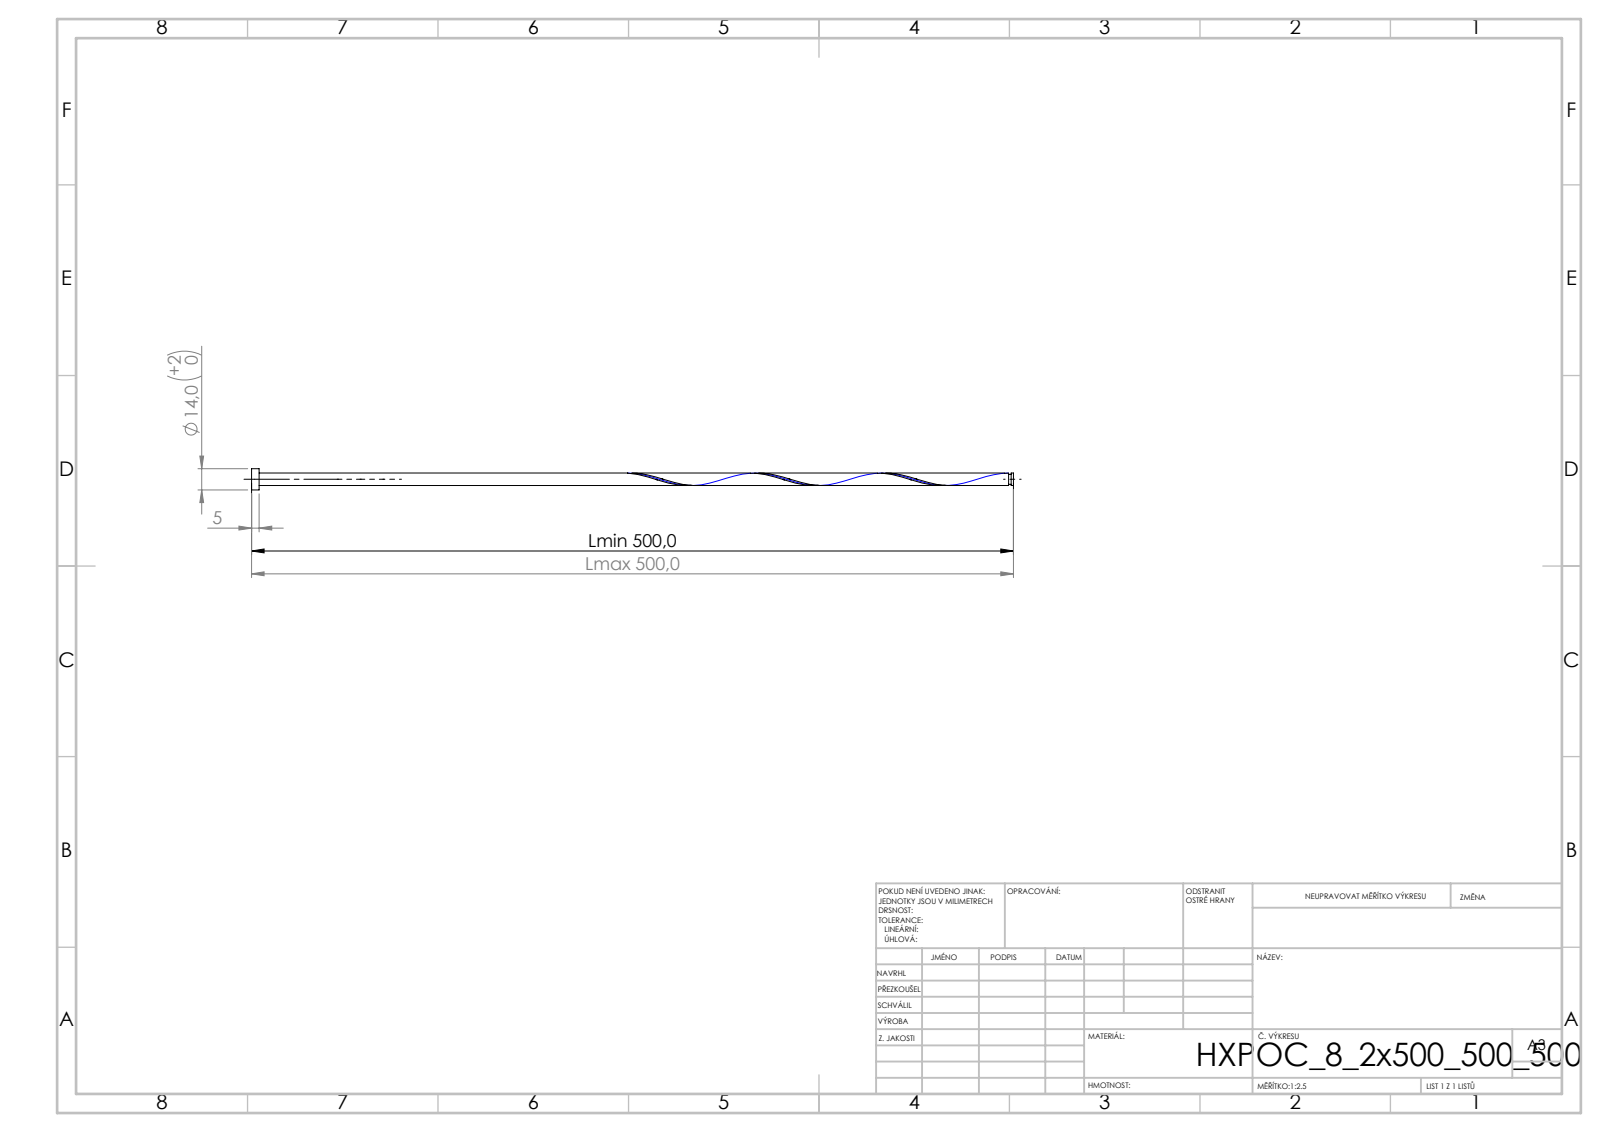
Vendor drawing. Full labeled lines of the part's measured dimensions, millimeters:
STEP written by: SolidWorks 2019 (CONFIG_CONTROL_DESIGN)
Units: millimetres
Bodies: 1 solid, 16 faces (6 planar, 9 cylindrical, 1 other)
Overall size (bounding box): 500 × 14 × 14
Volume: 32 494 mm³ · Surface area: 17 808 mm²
Round bosses / shafts (diameter × count): ⌀14 ×1, ⌀8.2 ×1, ⌀6.56 ×1
Main face-to-face distances: 5, 500, 495, 498.47, 493.47, 1.53, 496.83, 491.83, 1.64, 3.17
